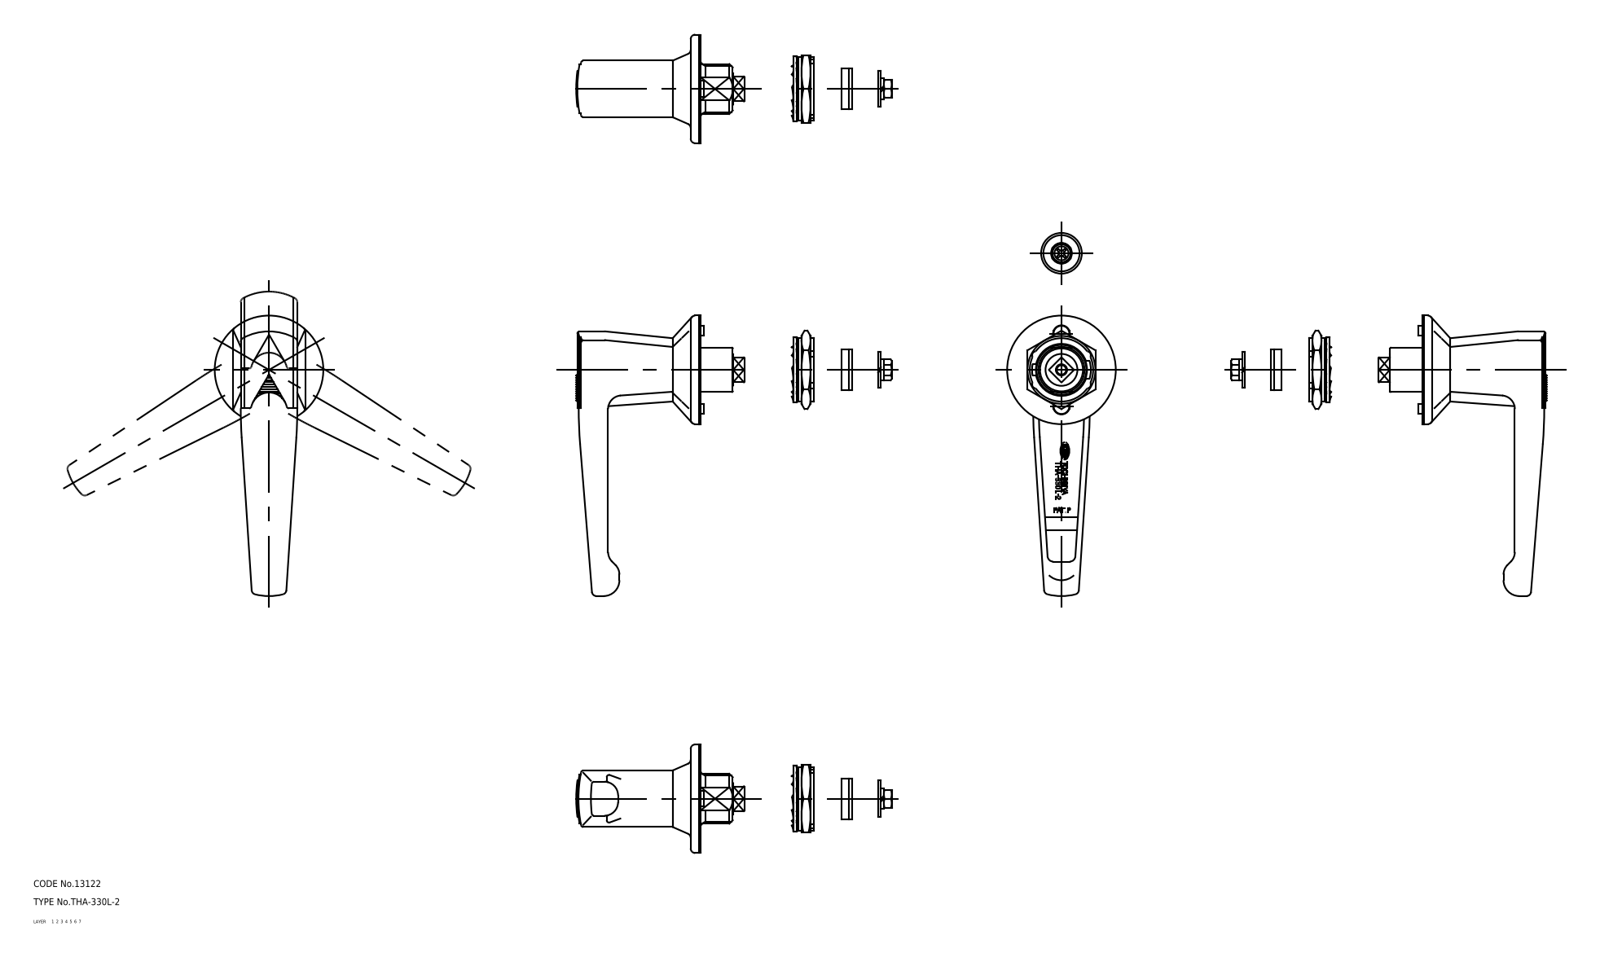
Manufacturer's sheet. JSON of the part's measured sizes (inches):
{"part_name": "washer_D; washer_C; washer_B; washer_A (+6 more)", "step_written_by": "CADfix (AUTOMOTIVE_DESIGN)", "units": "inches", "bodies": {"solids": 9, "faces": 326, "planar": 0, "cylindrical": 0, "other": 326}, "overall_size": [4.882, 3.165, 1.89], "volume_in3": 3.983, "surface_area_in2": 42.3}
